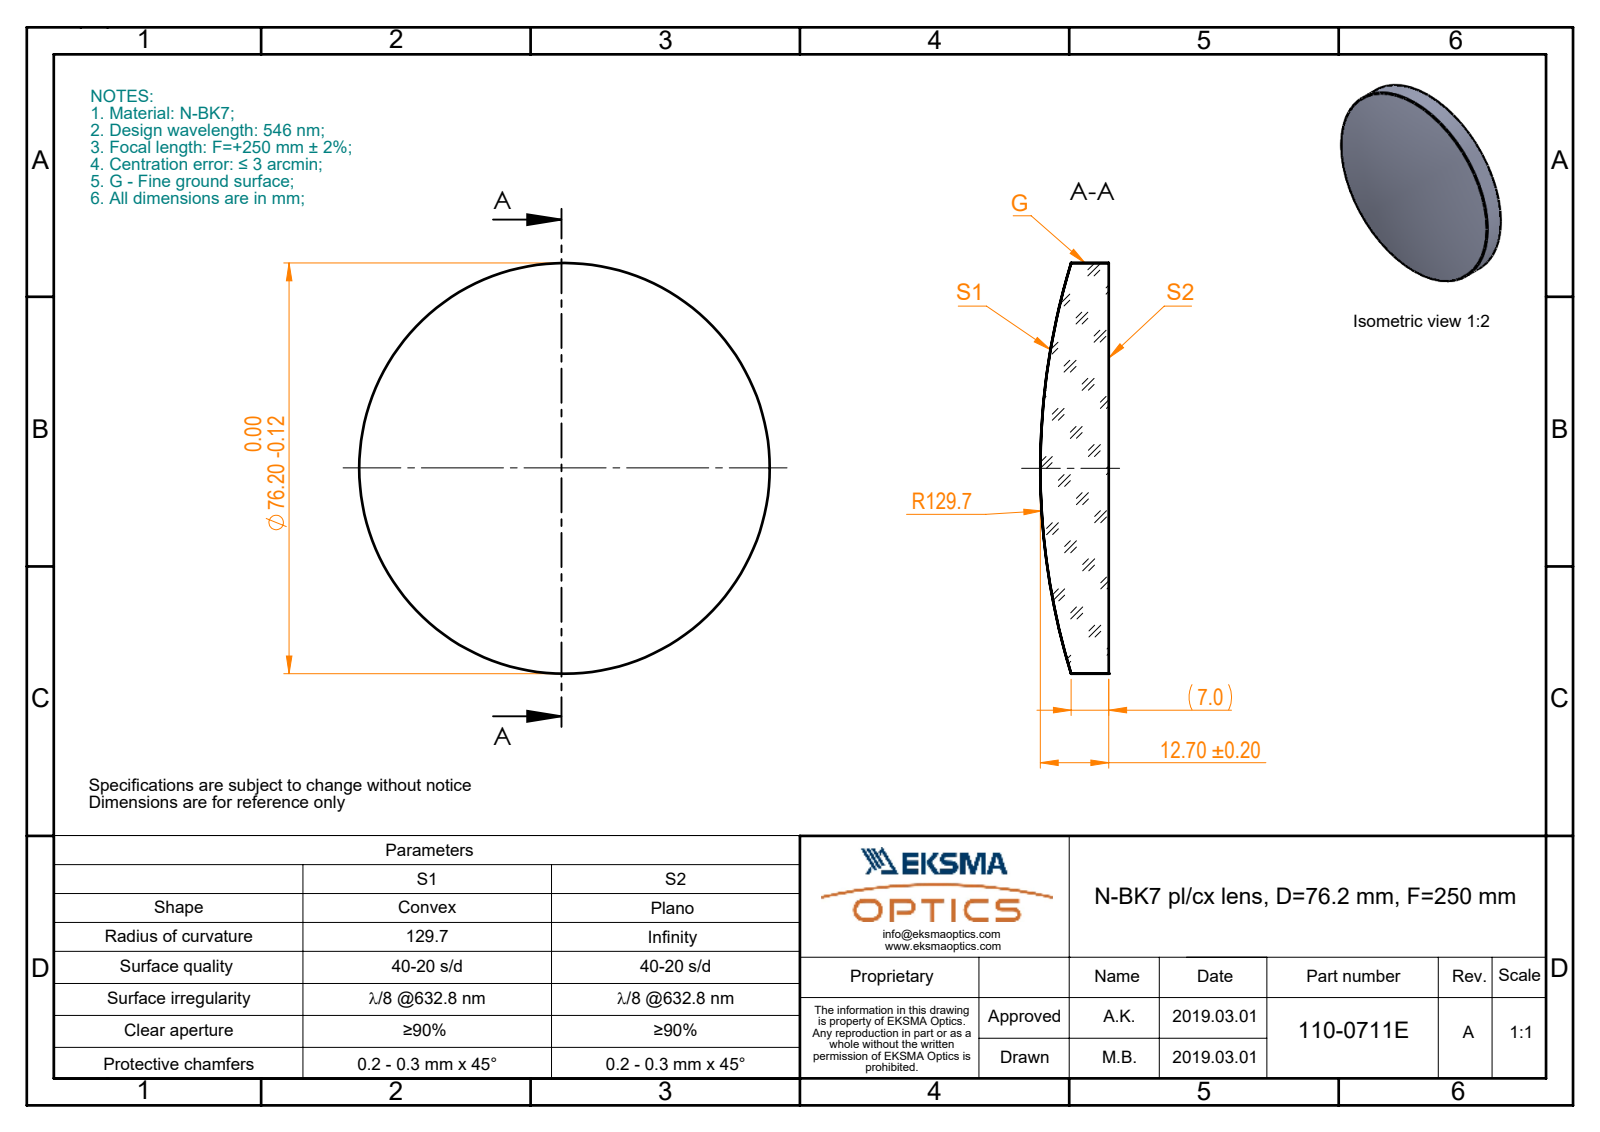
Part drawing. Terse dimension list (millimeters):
name: 110-0711E BK7 pl-cx 76.2 F250
written by: SolidWorks 2017 (CONFIG_CONTROL_DESIGN)
unit: mm
bodies: 1 solid, 5 faces (1 planar, 2 cylindrical, 2 other)
size: 76.2 × 76.2 × 12.7
volume: 44 967 mm³; area: 10 894 mm²
bosses: 1× ⌀76.2
